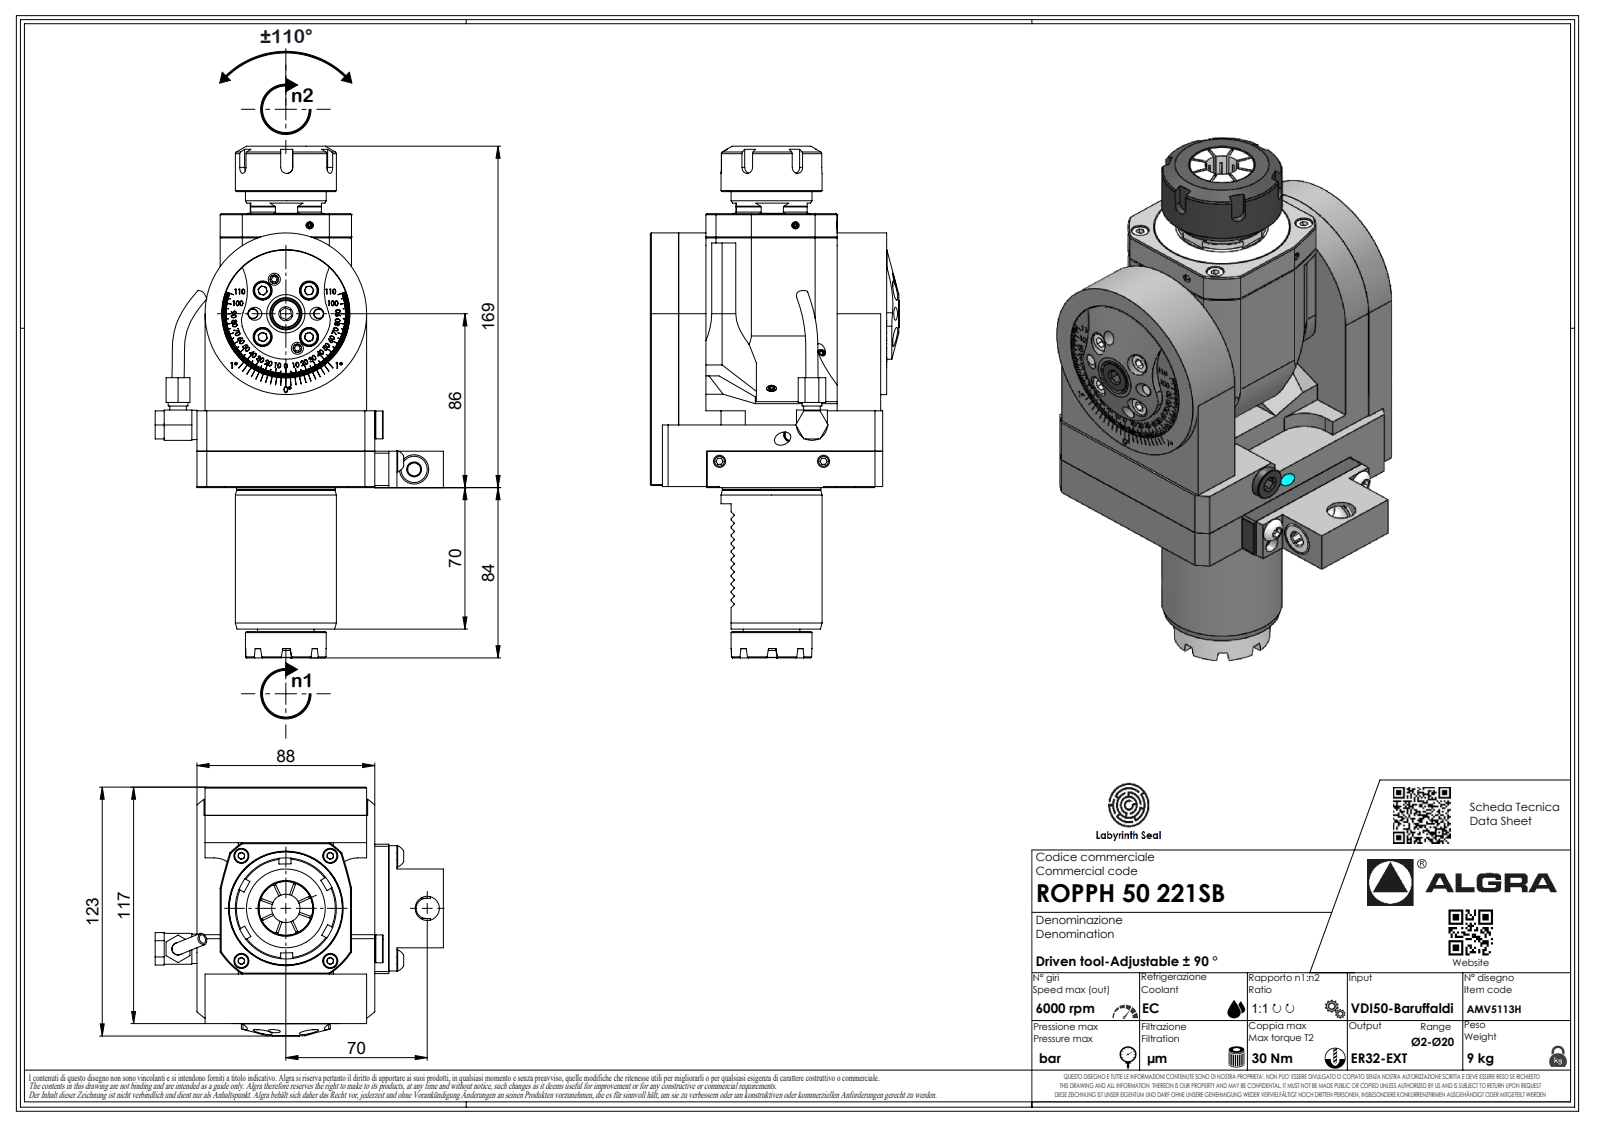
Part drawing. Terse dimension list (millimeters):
name: ROPPH50221SB
written by: SolidWorks 2023 (AUTOMOTIVE_DESIGN)
unit: mm
bodies: 1 solid, 676 faces (416 planar, 121 cylindrical, 139 other)
size: 253.16 × 142.7 × 123
volume: 1 277 000 mm³; area: 113 349 mm²
holes: 1× ⌀2.1
bosses: 1× ⌀80, 1× ⌀50, 1× ⌀48.7, 1× ⌀40, 1× ⌀28, 1× ⌀20.3, 1× ⌀14.5, 1× ⌀9.8
rounds: 16× R0.2, 12× R0.3, 7× R0.33, 7× R0.52, 7× R3.7, 5× R3, 4× R1, 2× R10
face distances: 4, 65, 84, 0.5, 76.5, 11.5, 22.5, 27.5, 7.5, 72.5
